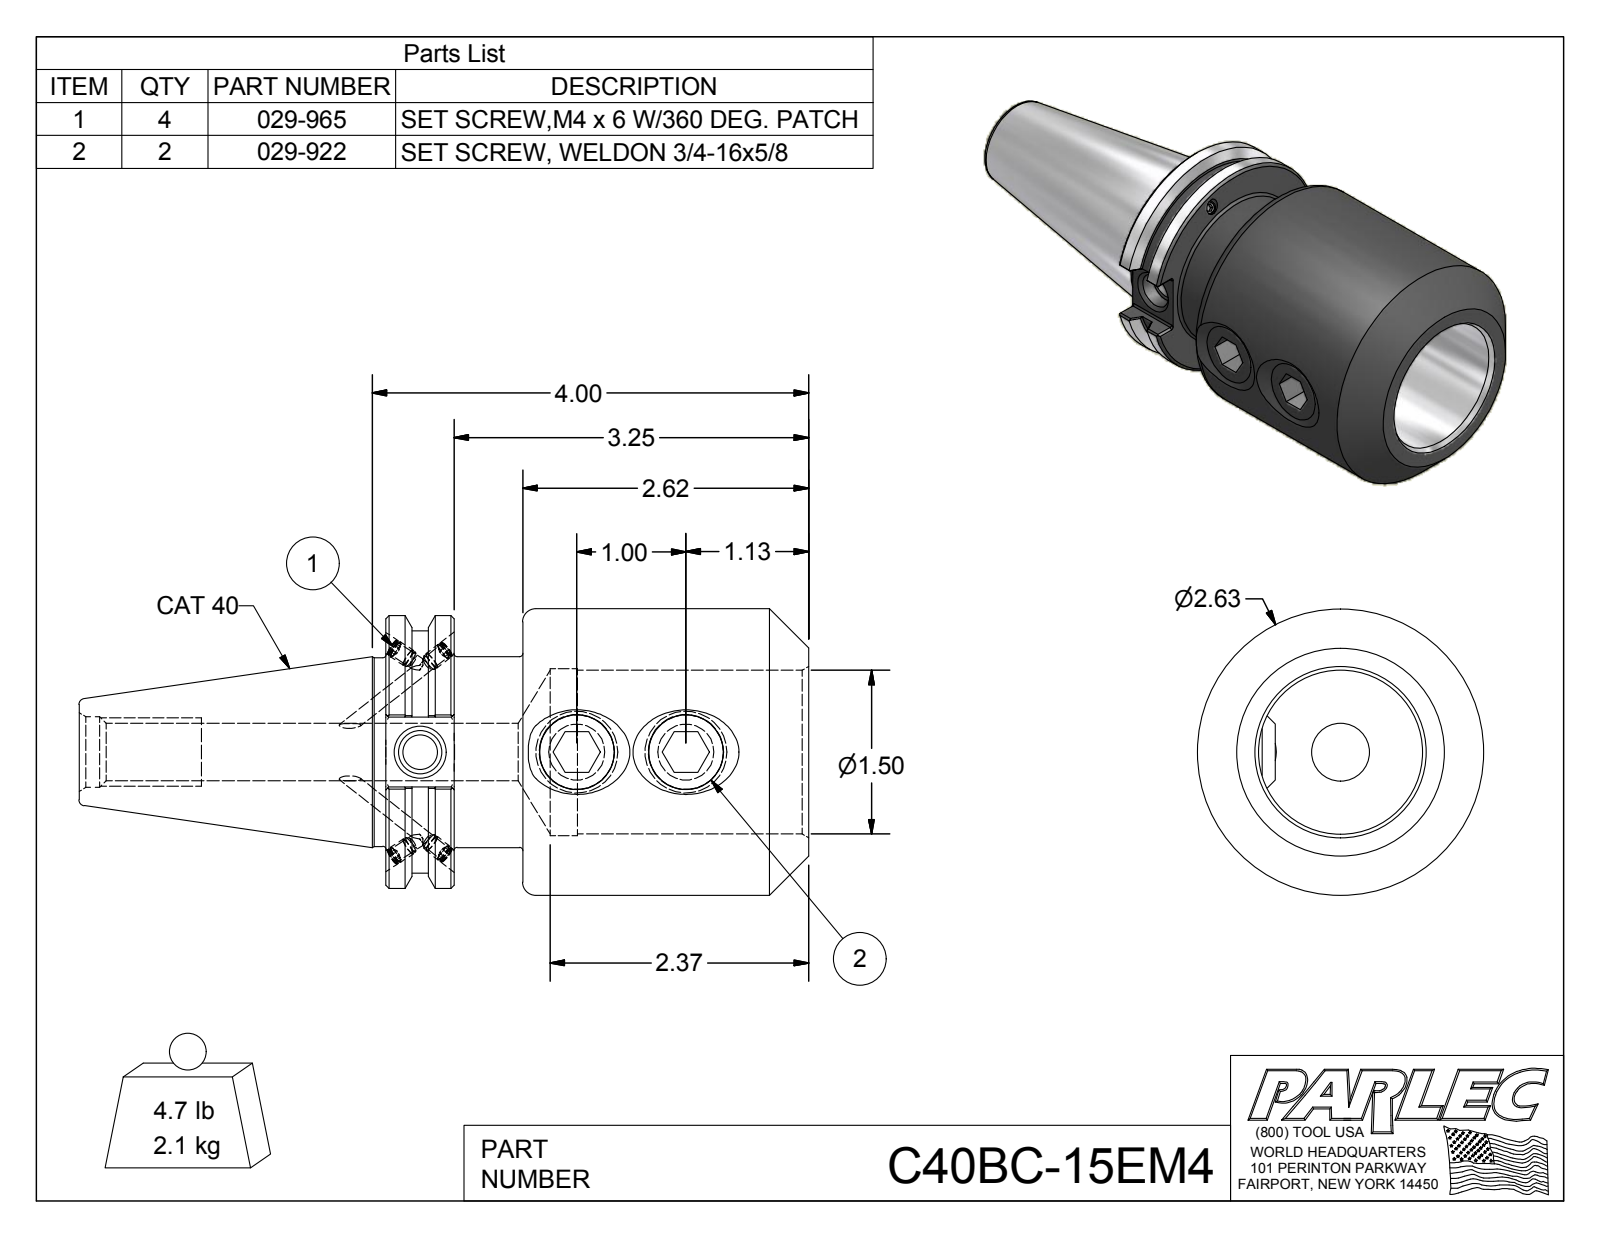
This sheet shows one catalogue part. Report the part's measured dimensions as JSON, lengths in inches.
{"part_name": "C40BC-15EM4; C40BC-15EM4-1; 029-922; 029-965", "step_written_by": "Autodesk Inventor 2012 (AUTOMOTIVE_DESIGN)", "units": "inches", "bodies": {"solids": 7, "faces": 199, "planar": 96, "cylindrical": 51, "other": 52}, "overall_size": [6.687, 2.625, 2.625], "volume_in3": 16.69, "surface_area_in2": 80.24, "round_holes": [[0.13, 4], [0.161, 4], [0.682, 2], [0.315, 1], [0.399, 1], [0.527, 1], [0.648, 1], [1.5, 1], [1.53, 1]], "round_bosses_or_shafts": [[0.165, 4], [0.157, 4], [0.75, 2], [2.625, 1], [2.5, 1], [2.219, 1], [1.75, 1], [1.73, 1]], "partial_cylinders_radius": [[0.02, 12]], "face_to_face_distances": [1.255, 0.625, 0.63, 3.875, 3.25, 2.62, 0.625, 0.375, 1.489, 2.114], "hole_center_spacings": [1, 1.435, 2.435]}
